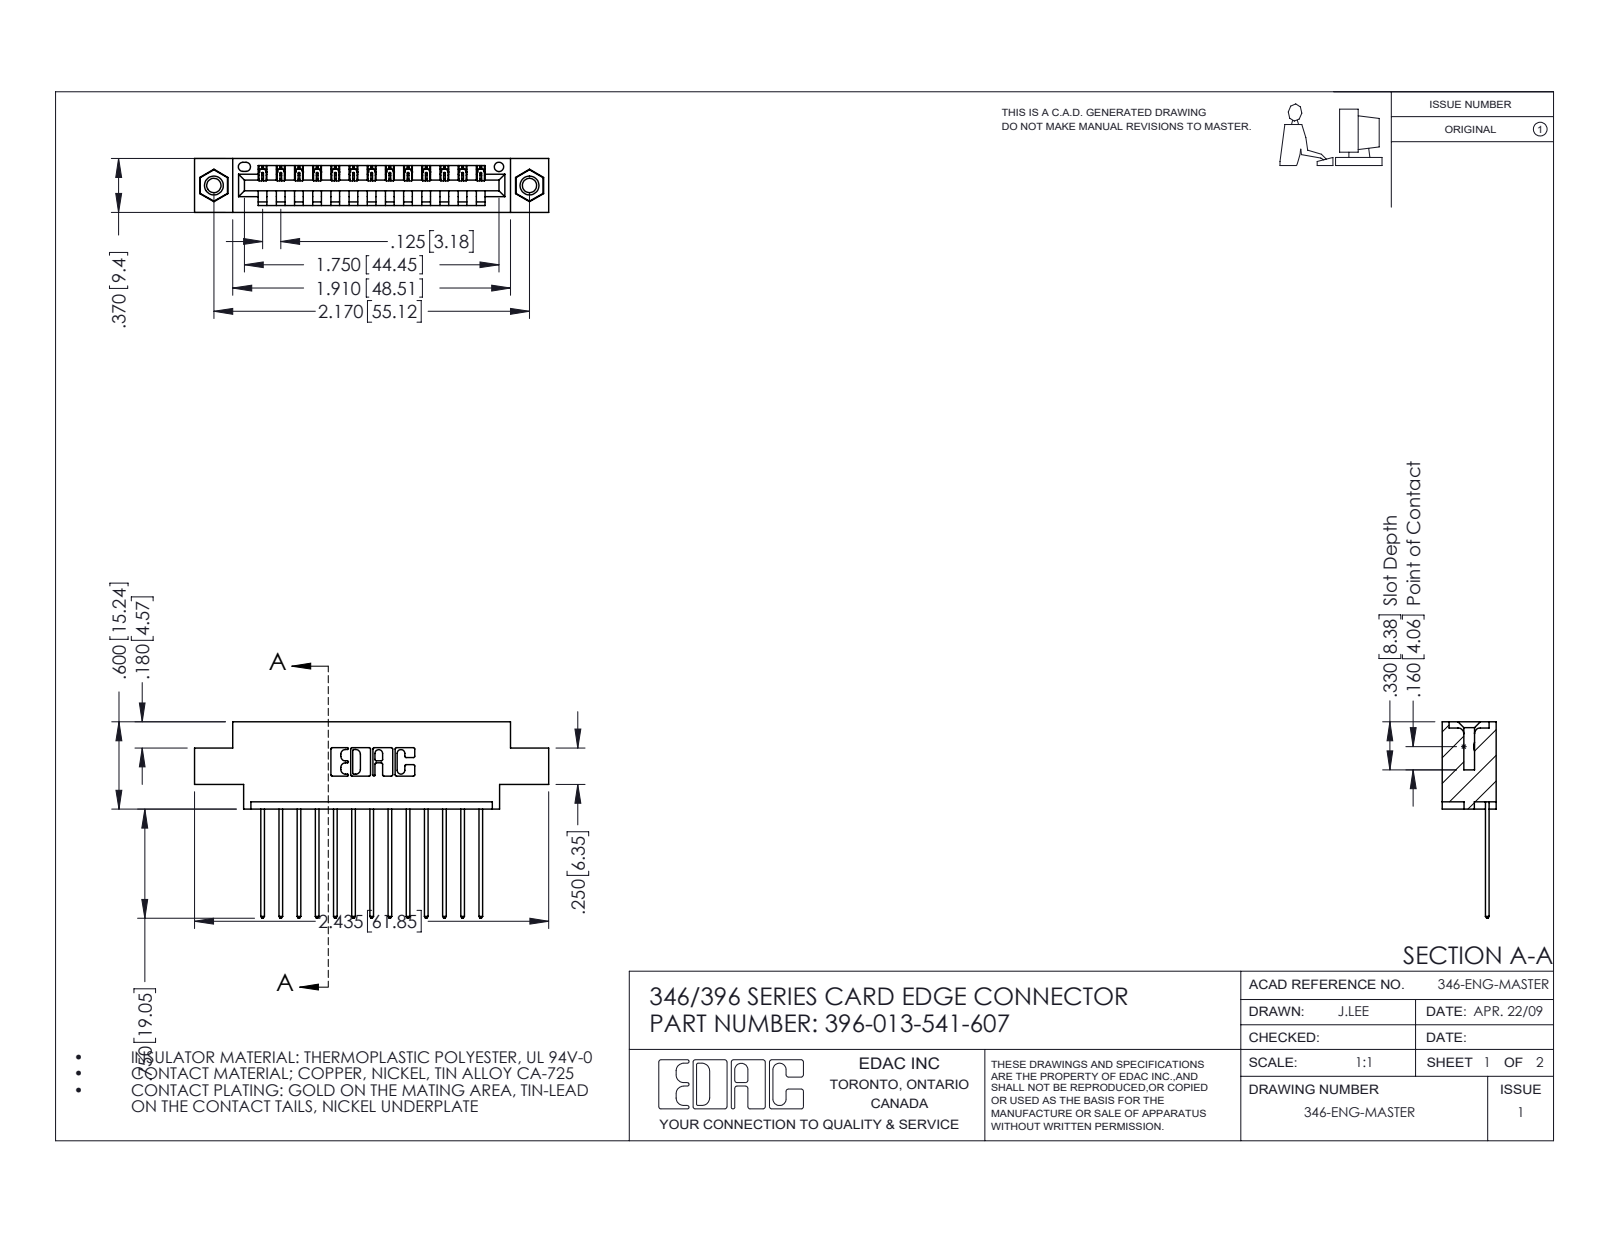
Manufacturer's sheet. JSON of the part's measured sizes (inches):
{"part_name": "345-292-001_345-293-141; 396-013-541-607; 345-250-001_345-250-005-103; 346 Part_0.170 Offset - 0.156 Dia-TI", "step_written_by": "SolidWorks 2016 (CONFIG_CONTROL_DESIGN)", "units": "inches", "bodies": {"solids": 16, "faces": 940, "planar": 632, "cylindrical": 292, "other": 16}, "overall_size": [2.435, 1.35, 0.37], "volume_in3": 0.341, "surface_area_in2": 11.05, "round_holes": [[0.098, 2], [0.125, 2], [0.156, 2], [0.064, 1]], "round_bosses_or_shafts": [[0.155, 2]], "partial_cylinders_radius": [[0.006, 26], [0.01, 26], [0.01, 22], [0.007, 6], [0.031, 6], [0.026, 3], [0.031, 2], [0.04, 2]], "face_to_face_distances": [0.048, 0.322, 0.25, 0.37, 0.072, 0.298, 0.025, 0.222, 0.148, 0.1], "hole_center_spacings": [0.246, 1.964, 2.17]}
